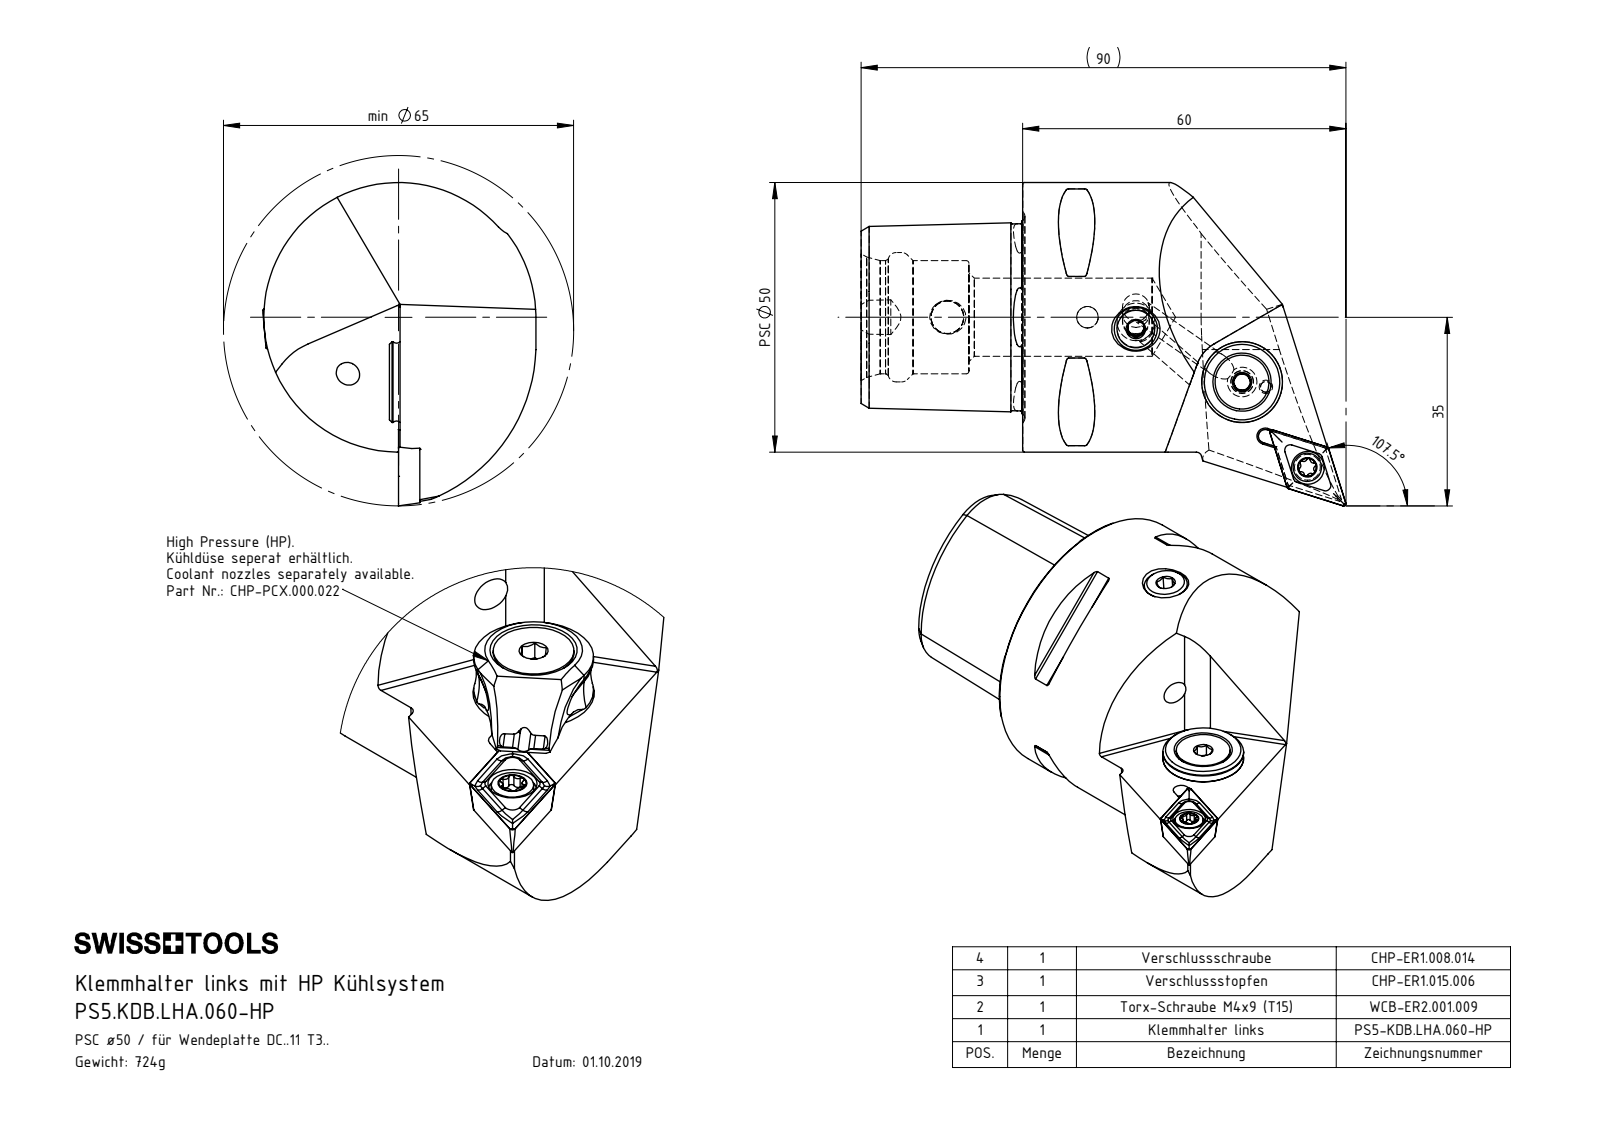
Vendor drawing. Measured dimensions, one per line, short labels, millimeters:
name: CHP-ER1.015.006_A; CHP-ER1.015.006; DIN 3771 - 13x1; DIN 7991 - M5x15 (+6 more)
written by: SolidWorks 2017 (AUTOMOTIVE_DESIGN)
unit: mm
bodies: 8 solids, 374 faces (90 planar, 98 cylindrical, 186 other)
size: 90.01 × 60 × 50.71
volume: 92 319 mm³; area: 21 292 mm²
holes: 3× ⌀4.2, 2× ⌀6.1, 1× ⌀1.2, 1× ⌀2, 1× ⌀2.5, 1× ⌀3, 1× ⌀3.3, 1× ⌀4, 1× ⌀4.4, 1× ⌀5, 1× ⌀5.2, 1× ⌀7
bosses: 1× ⌀50, 1× ⌀15, 1× ⌀13.4, 1× ⌀10, 1× ⌀8, 1× ⌀5.5, 1× ⌀5.25, 1× ⌀5
rounds: 10× R0.5, 6× R0.34, 6× R0.59, 1× R1.25, 1× R4, 1× R7, 1× R25.5, 1× R31
face distances: 30, 4.5, 19.18, 0.83, 3.67, 44.4, 10, 20, 20.7, 21.53
hole spacings: 4.5, 16.78, 16.9, 19.92, 20.04, 26, 31.13, 35.56
